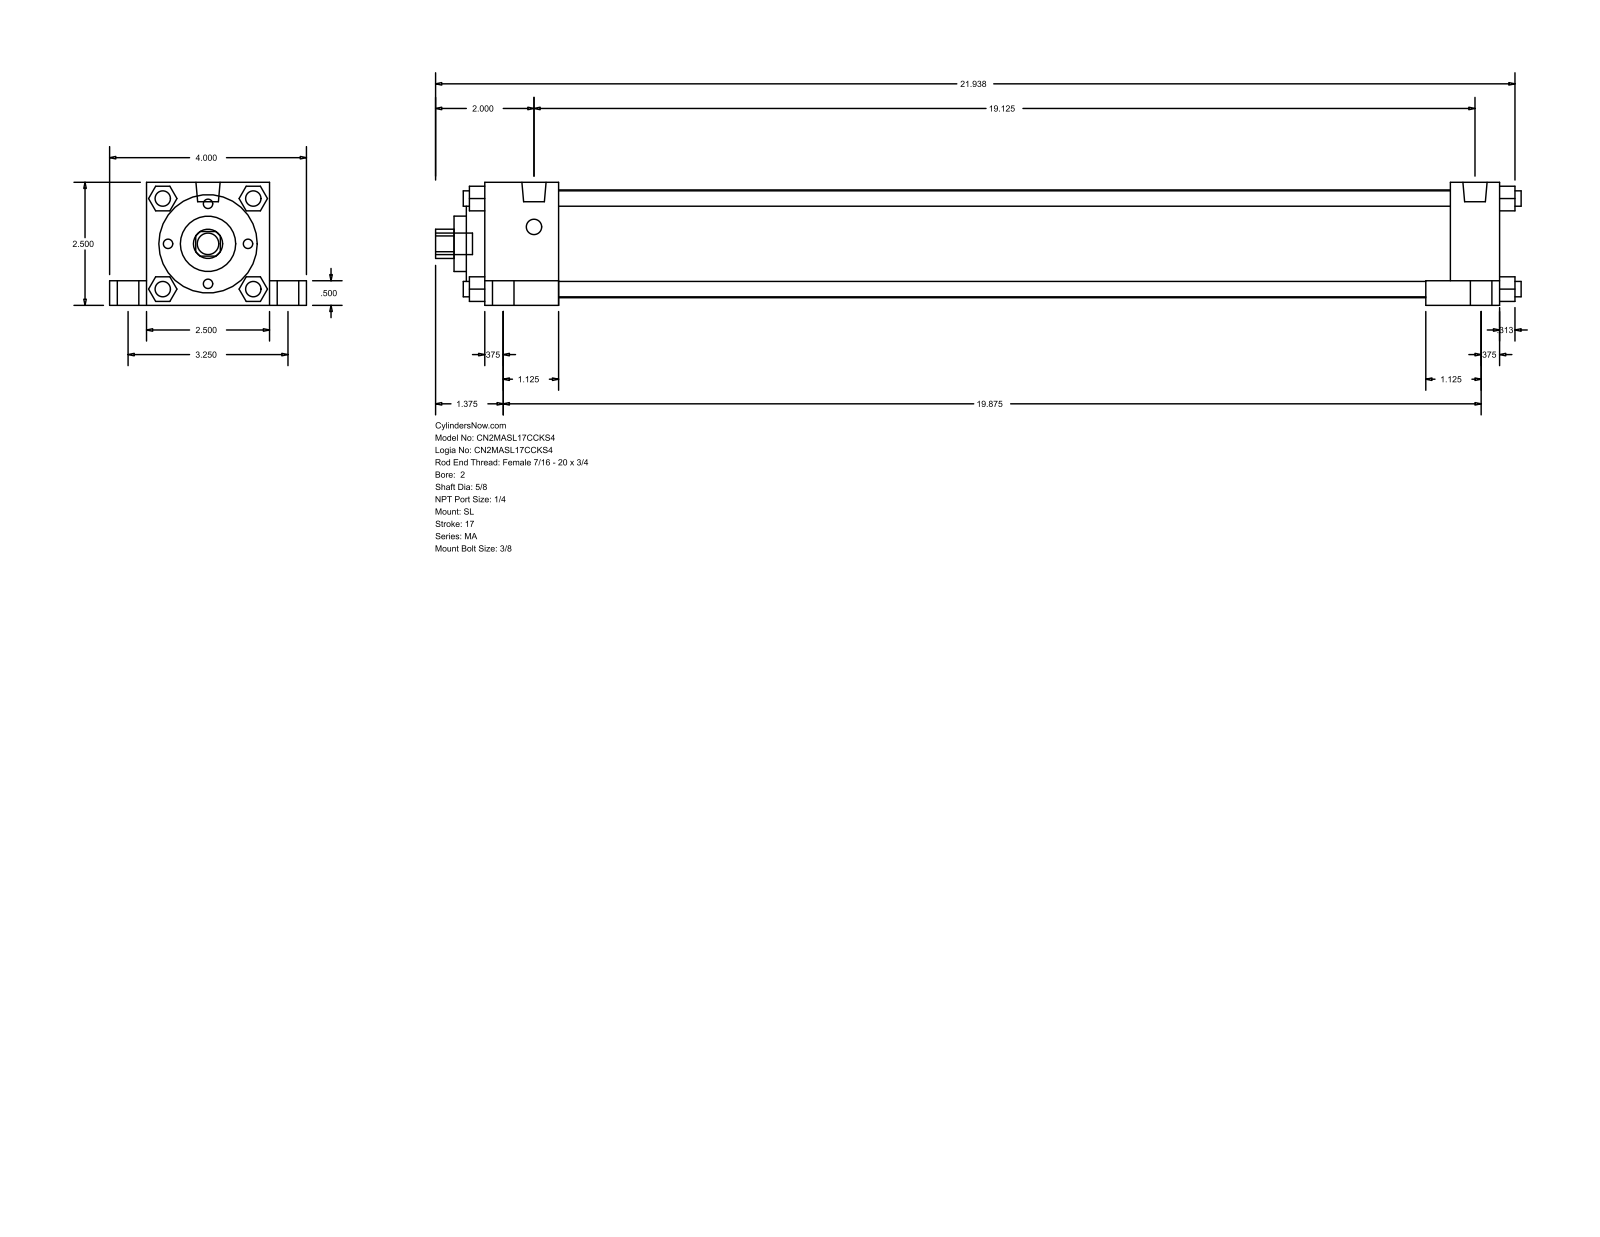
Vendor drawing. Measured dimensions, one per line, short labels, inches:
name: MA_SL__0200_0.625
written by: GSSL Pune (CONFIG_CONTROL_DESIGN)
unit: in
bodies: 0 solids, 150 faces (113 planar, 37 cylindrical, 0 other)
size: 22.063 × 4 × 2.5
holes: 1× ⌀0.625, 1× ⌀1.125, 1× ⌀2, 1× ⌀2.19
bosses: 8× ⌀0.313, 5× ⌀0.437, 4× ⌀0.687, 2× ⌀0.492
rounds: 1× R0.297
face distances: 2.5, 0.5, 0.375, 0.75, 3.25, 1.5, 2, 20.625, 19.125, 19.625
